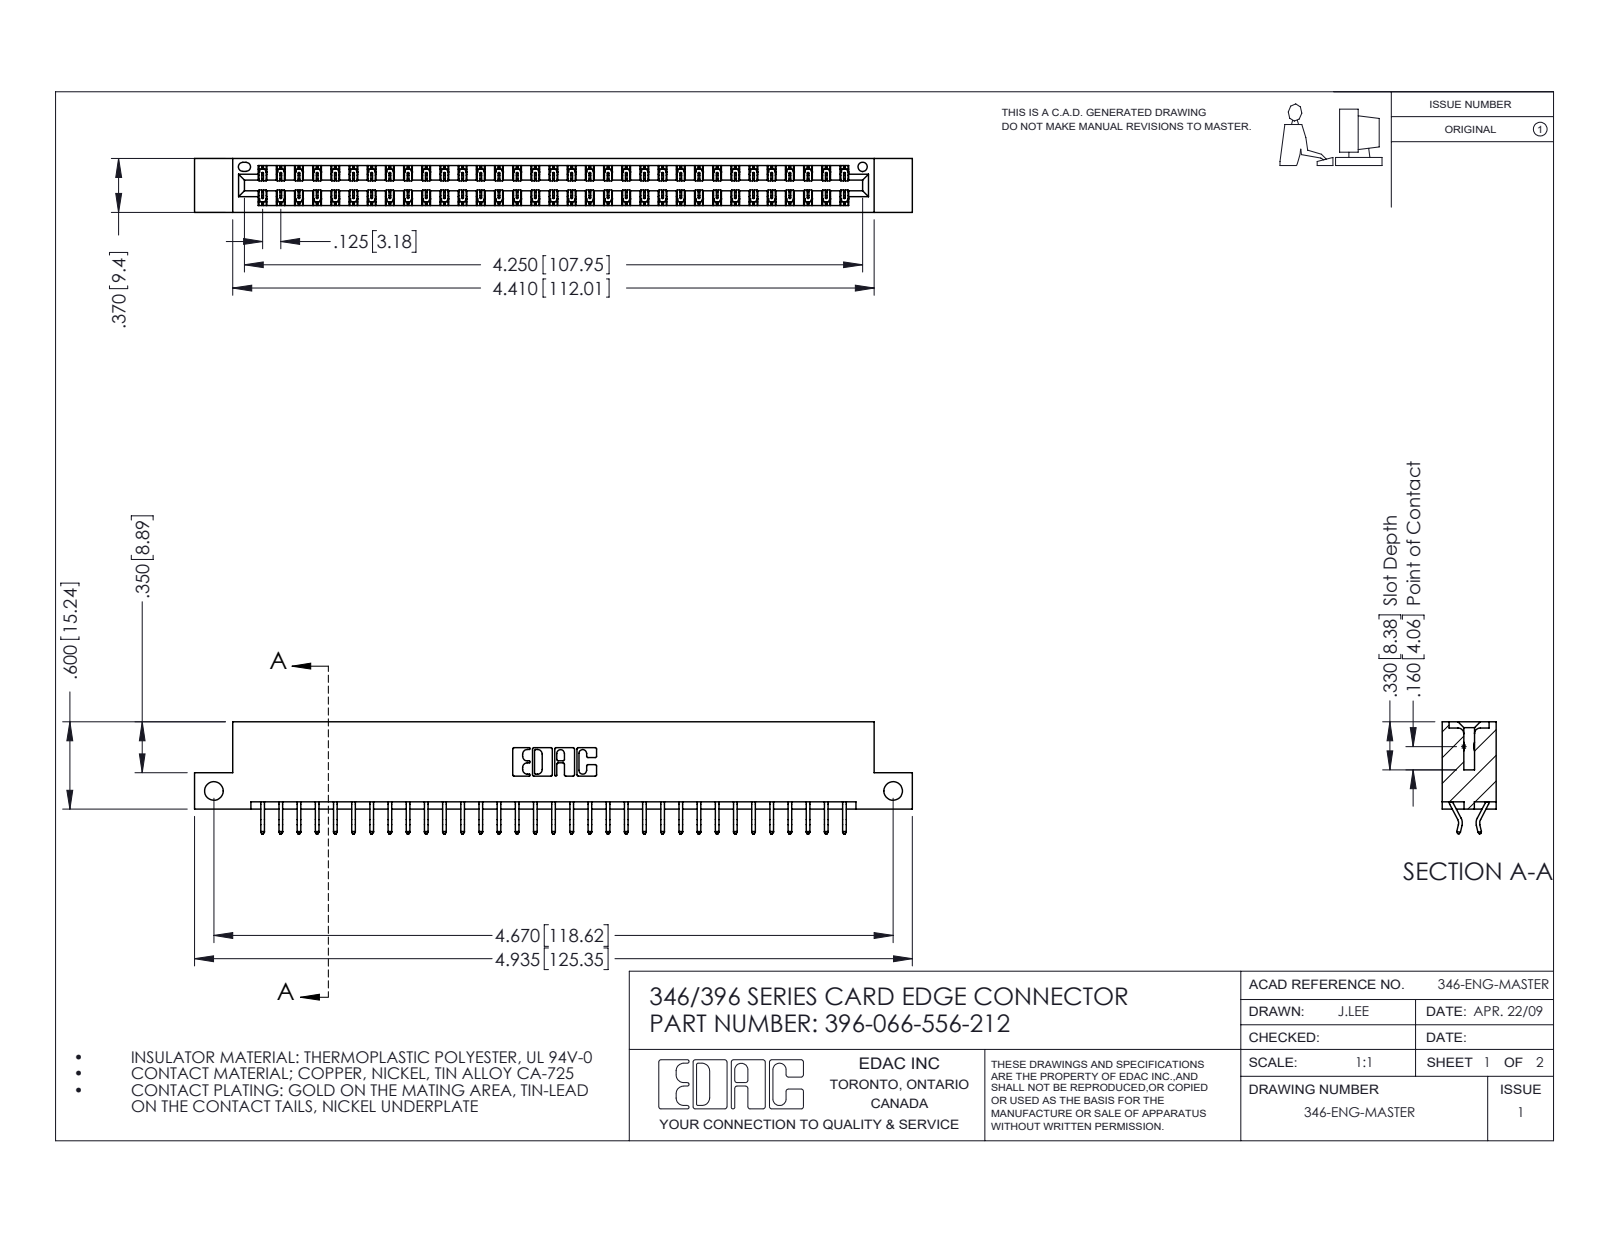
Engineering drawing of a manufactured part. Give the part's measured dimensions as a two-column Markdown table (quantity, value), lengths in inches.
| quantity | value |
| --- | --- |
| part name | 345-292-001_556 Tail; 346 Part_Flush Mounting Lugs - Side Mount; 396-066-556-212 |
| STEP written by | SolidWorks 2016 (CONFIG_CONTROL_DESIGN) |
| units | inches |
| bodies | 67 solids, 3950 faces (2650 planar, 1300 cylindrical, 0 other) |
| overall size | 4.935 × 0.77 × 0.37 |
| volume | 0.736 in³ |
| surface area | 25.17 in² |
| round holes (diameter × count) | 0.128 × 2, 0.064 × 1 |
| partial cylindrical surfaces (radius × count) | 0.006 × 99, 0.01 × 22, 0.007 × 6, 0.031 × 6, 0.026 × 3, 0.01 × 2, 0.014 × 2, 0.022 × 2 |
| main face-to-face distances | 0.048, 0.322, 0.37, 0.25, 0.025, 0.072, 0.298, 0.275, 0.148, 0.222 |
| hole center spacings | 4.67 |
